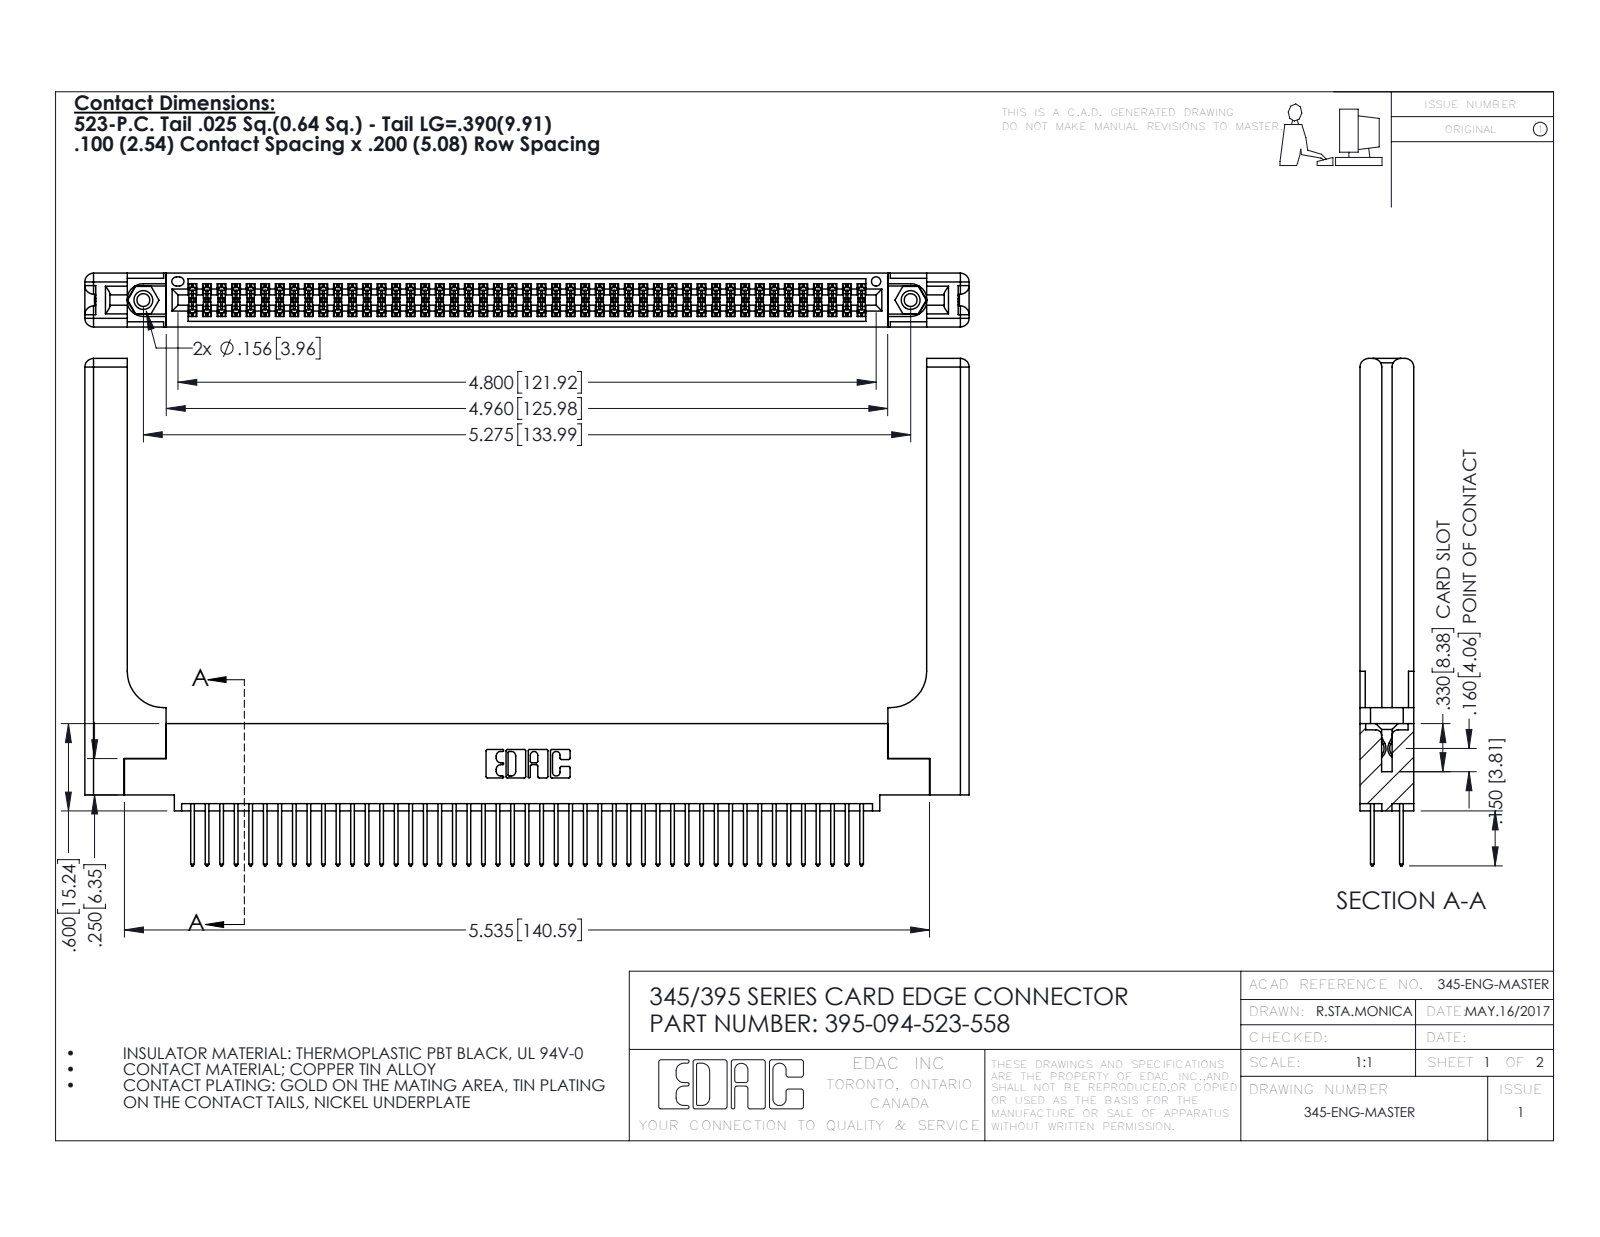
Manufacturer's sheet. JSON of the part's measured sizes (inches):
{"part_name": "345-292-001_345-293-123; 345 Part_0.110 Offset - 0.156 Dia-TH; 395-094-523-558; 345-220-058_345-220-058 (+1 more)", "step_written_by": "SolidWorks 2016 (CONFIG_CONTROL_DESIGN)", "units": "inches", "bodies": {"solids": 99, "faces": 5086, "planar": 3334, "cylindrical": 1692, "other": 60}, "overall_size": [6.079, 3.487, 0.37], "volume_in3": 1.443, "surface_area_in2": 44.22, "round_holes": [[0.089, 2], [0.125, 2], [0.156, 2], [0.064, 1]], "round_bosses_or_shafts": [[0.155, 2]], "partial_cylinders_radius": [[0.006, 141], [0.01, 94], [0.01, 22], [0.06, 16], [0.007, 6], [0.031, 6], [0.026, 3], [0.014, 2]], "face_to_face_distances": [0.072, 0.298, 0.37, 0.098, 0.272, 0.025, 0.2, 0.225, 0.175, 0.148], "hole_center_spacings": [0.27, 5.039, 5.275]}
